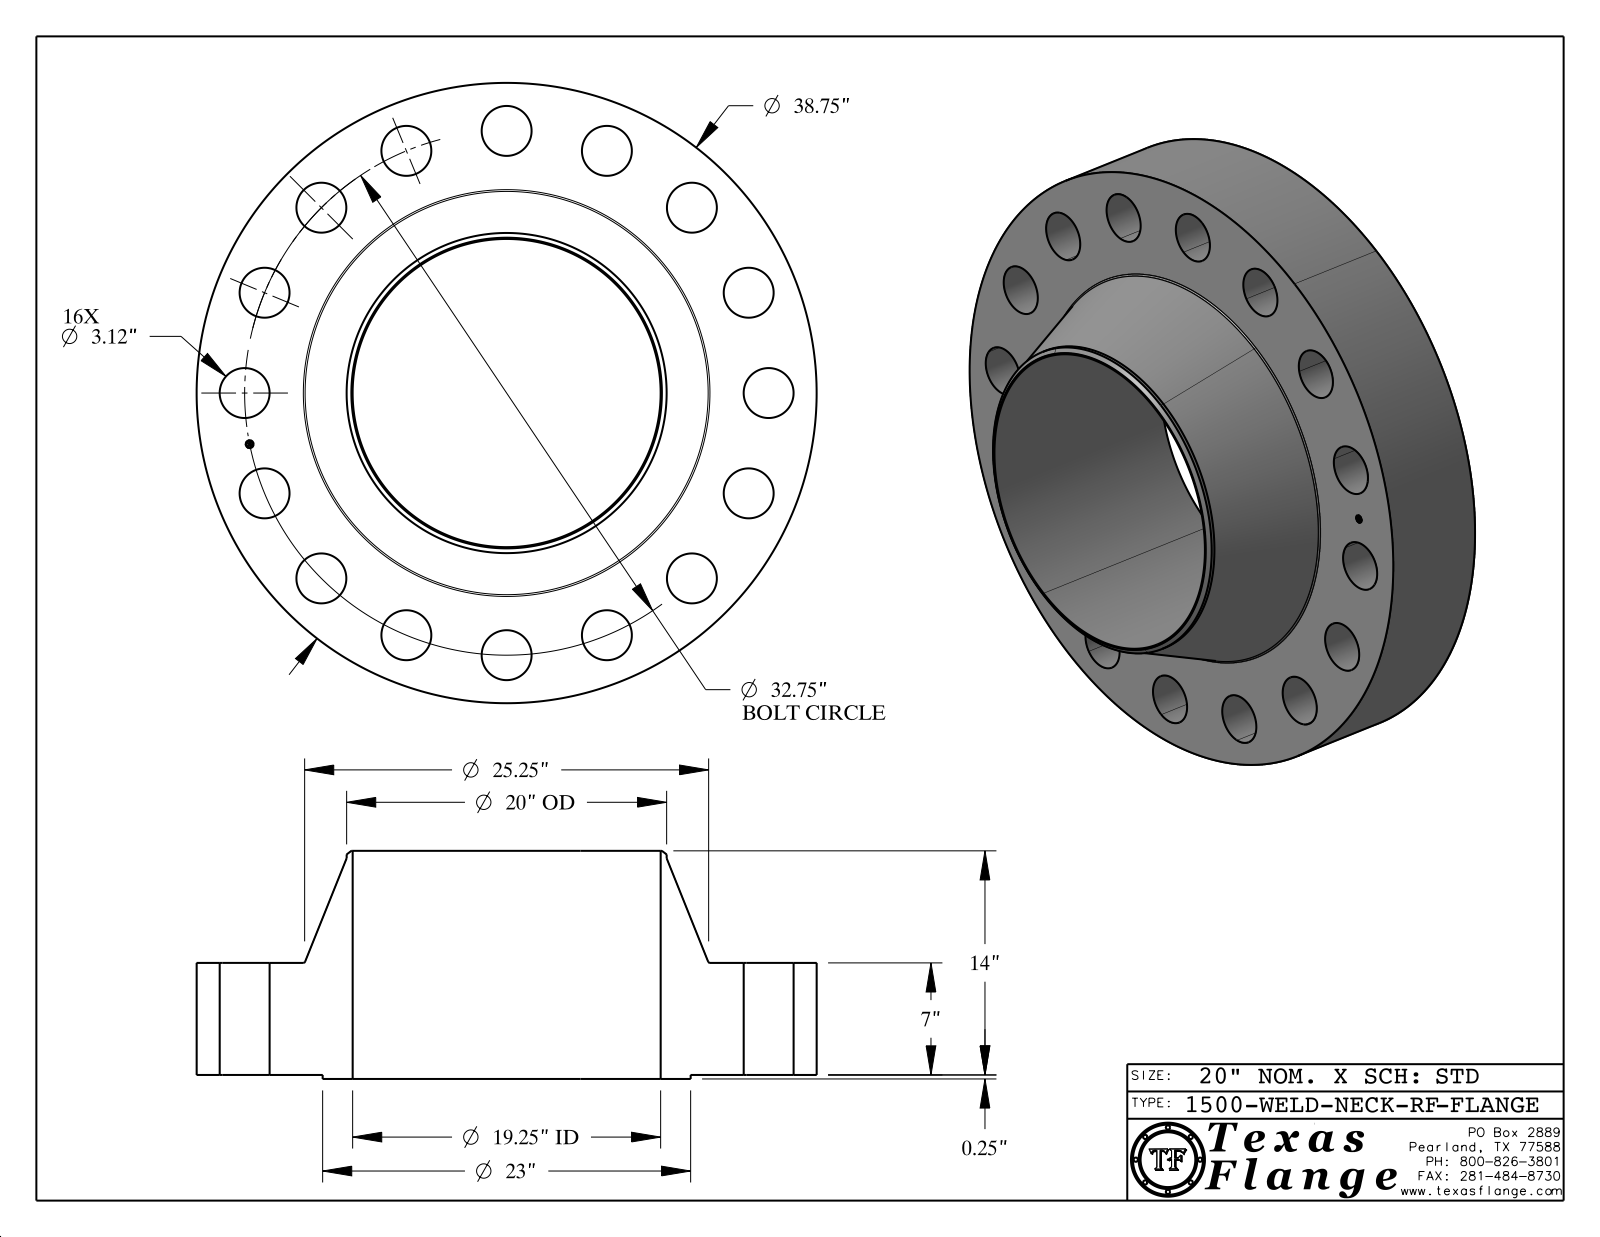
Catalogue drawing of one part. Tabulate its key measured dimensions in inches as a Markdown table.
| quantity | value |
| --- | --- |
| part name | 1500-WELD-NECK-RF |
| STEP written by | CATIA V5 STEP AP214 (AUTOMOTIVE_DESIGN) |
| units | inches |
| bodies | 1 solid, 435 faces (369 planar, 60 cylindrical, 6 other) |
| overall size | 38.75 × 38.75 × 14.25 |
| volume | 6 139 in³ |
| surface area | 4 694 in² |
| round holes (diameter × count) | 3.12 × 16, 0.495 × 1, 19.25 × 1 |
| round bosses / shafts (diameter × count) | 0.03 × 8, 38.75 × 1, 23 × 1, 20 × 1, 0.39 × 1 |
| main face-to-face distances | 7, 0.25, 7.25, 14.25, 14, 7.235, 6.985, 0.015, 7.015, 0.148 |
| hole center spacings | 18.195, 16.375, 12.533, 23.157, 30.257, 6.389, 6.389, 27.23 |
